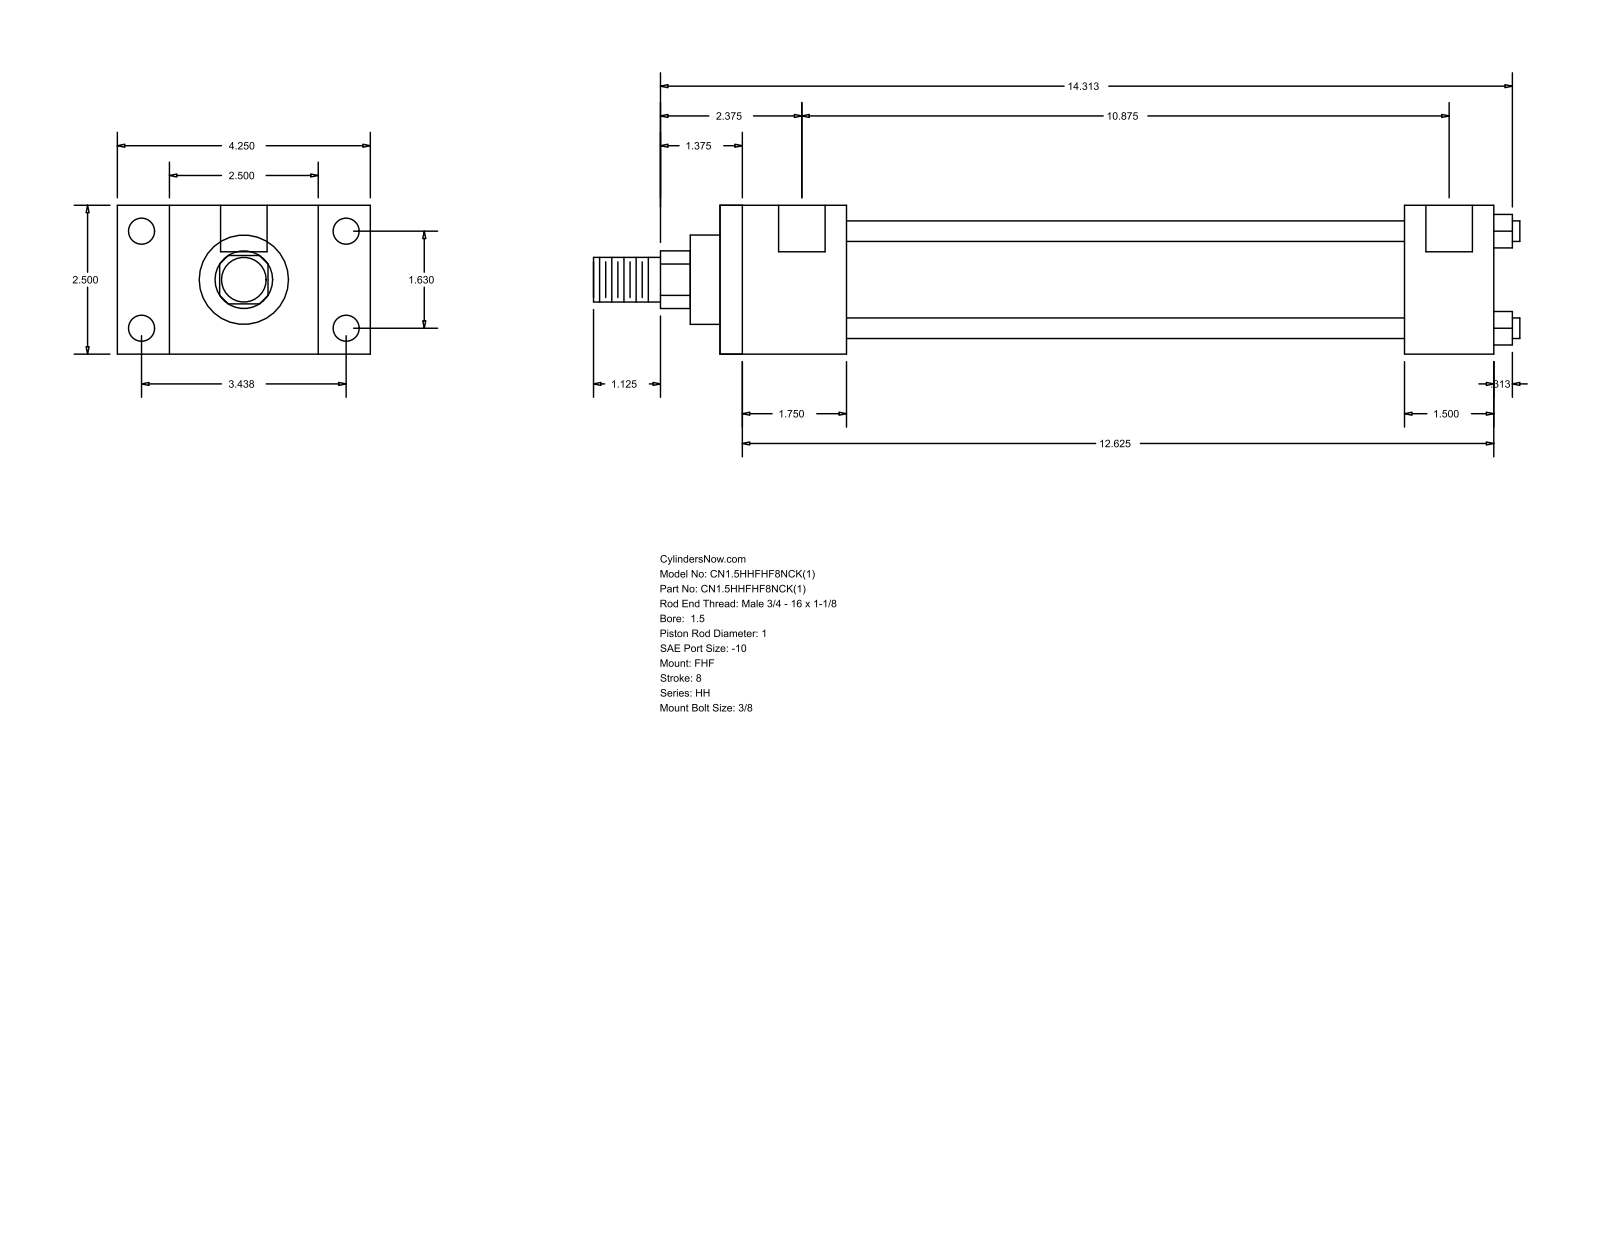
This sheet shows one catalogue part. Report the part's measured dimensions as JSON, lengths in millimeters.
{"part_name": "HH_FHF__0150_1", "step_written_by": "GSSL Pune (CONFIG_CONTROL_DESIGN)", "units": "millimeters", "bodies": {"solids": 0, "faces": 88, "planar": 60, "cylindrical": 28, "other": 0}, "overall_size": [395.29, 107.95, 63.5], "round_holes": [[5.56, 4], [11.13, 4], [19.84, 2]], "round_bosses_or_shafts": [[8.76, 4], [44.45, 1], [38.1, 1], [25.4, 1], [19.05, 1]], "partial_cylinders_radius": [[12.29, 1]], "face_to_face_distances": [63.5, 22.23, 85.73, 53.98, 107.96, 330.2, 276.22, 38.1, 292.1, 238.12], "hole_center_spacings": [1.59, 41.4, 87.32, 96.64, 277.81, 279.4, 276.22]}
